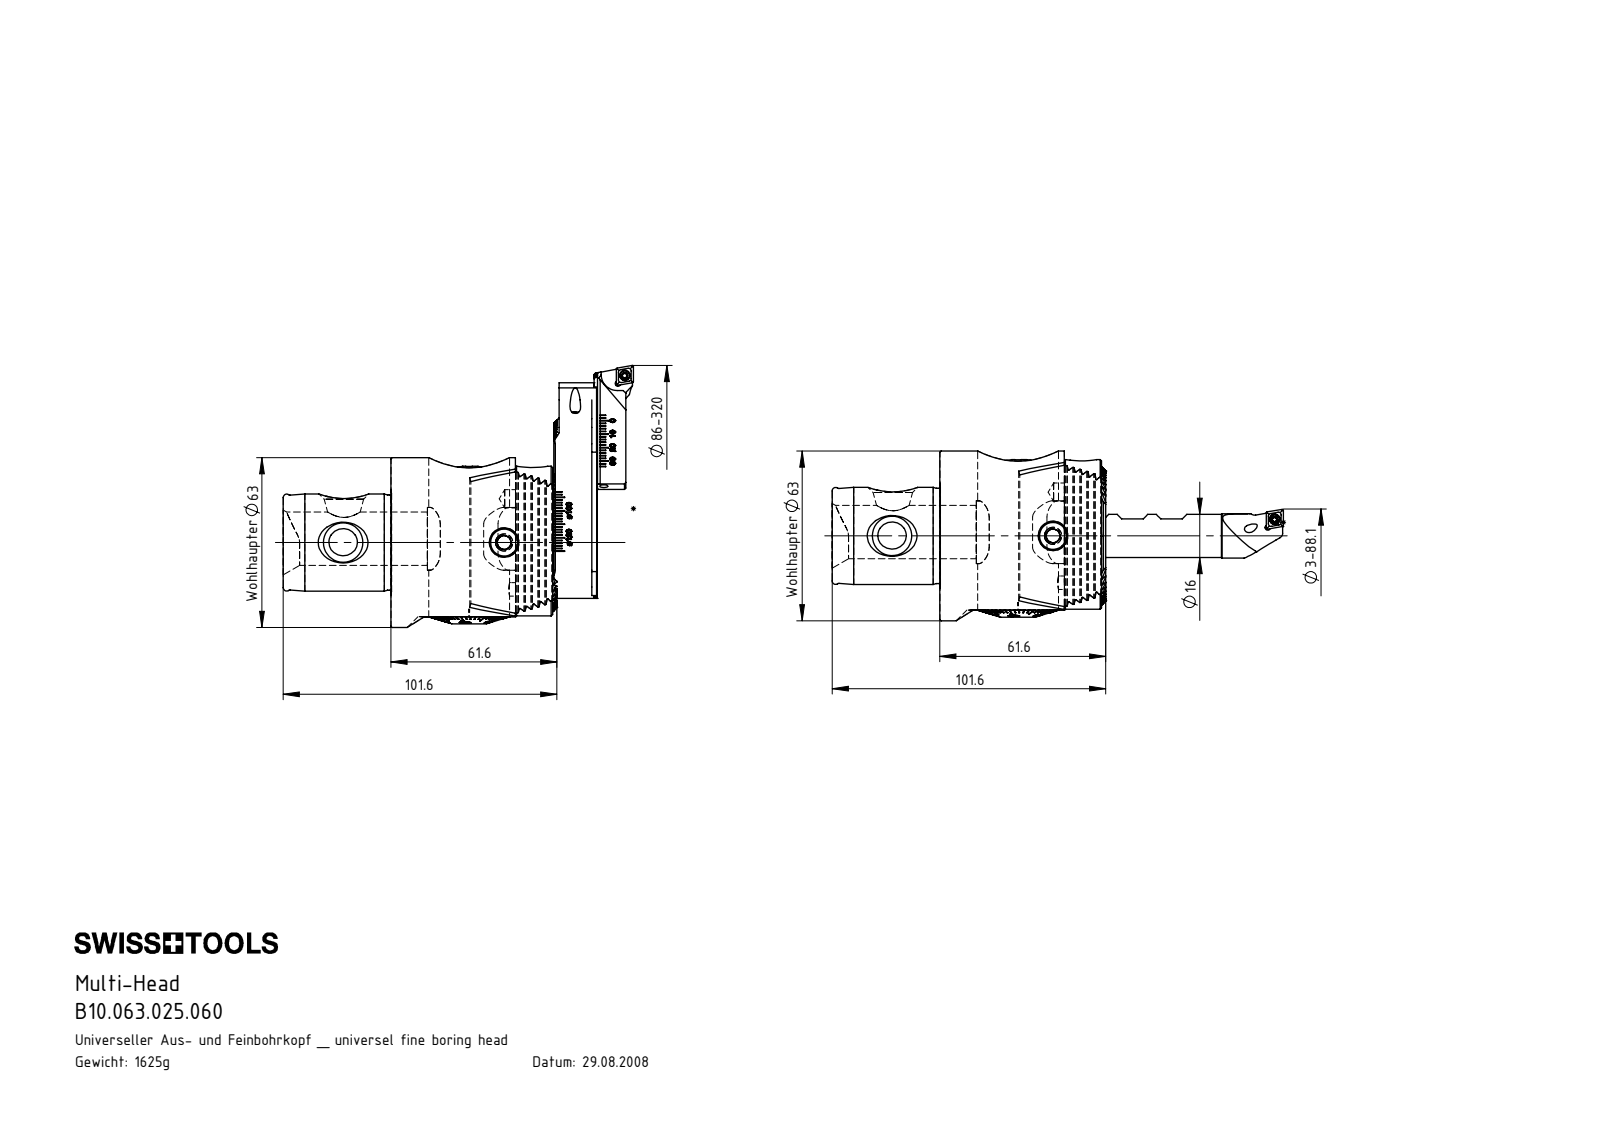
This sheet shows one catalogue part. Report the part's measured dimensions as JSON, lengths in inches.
{"part_name": "MH1-BG3.001.042_D; DIN 3771 - 25x1.5; MH1-BG1.001.049_B; ISO 4026 - M8 x 6 (+8 more)", "step_written_by": "SolidWorks 2017 (AUTOMOTIVE_DESIGN)", "units": "inches", "bodies": {"solids": 19, "faces": 973, "planar": 586, "cylindrical": 175, "other": 212}, "overall_size": [4.472, 2.48, 2.48], "volume_in3": 11.68, "surface_area_in2": 102.1, "round_holes": [[0.165, 5], [0.335, 4], [0.268, 3], [0.433, 3], [0.197, 2], [0.787, 2], [0.039, 1], [0.063, 1], [0.13, 1], [0.252, 1], [0.315, 1], [0.463, 1]], "round_bosses_or_shafts": [[0.433, 4], [0.335, 4], [0.197, 4], [0.394, 3], [2.48, 1], [1.417, 1], [1.39, 1], [1.181, 1]], "partial_cylinders_radius": [[0.006, 21], [0.008, 20], [0.236, 6], [0.157, 2], [0.335, 2], [1.22, 2], [0.079, 1], [0.276, 1]], "face_to_face_distances": [0.094, 1.835, 1.819, 0.016, 0.068, 0.188, 0.187, 0.341, 0.281, 0.205], "hole_center_spacings": [0.659, 0.71, 0.808, 0.945, 1.181, 1.37, 1.513, 0.287]}
